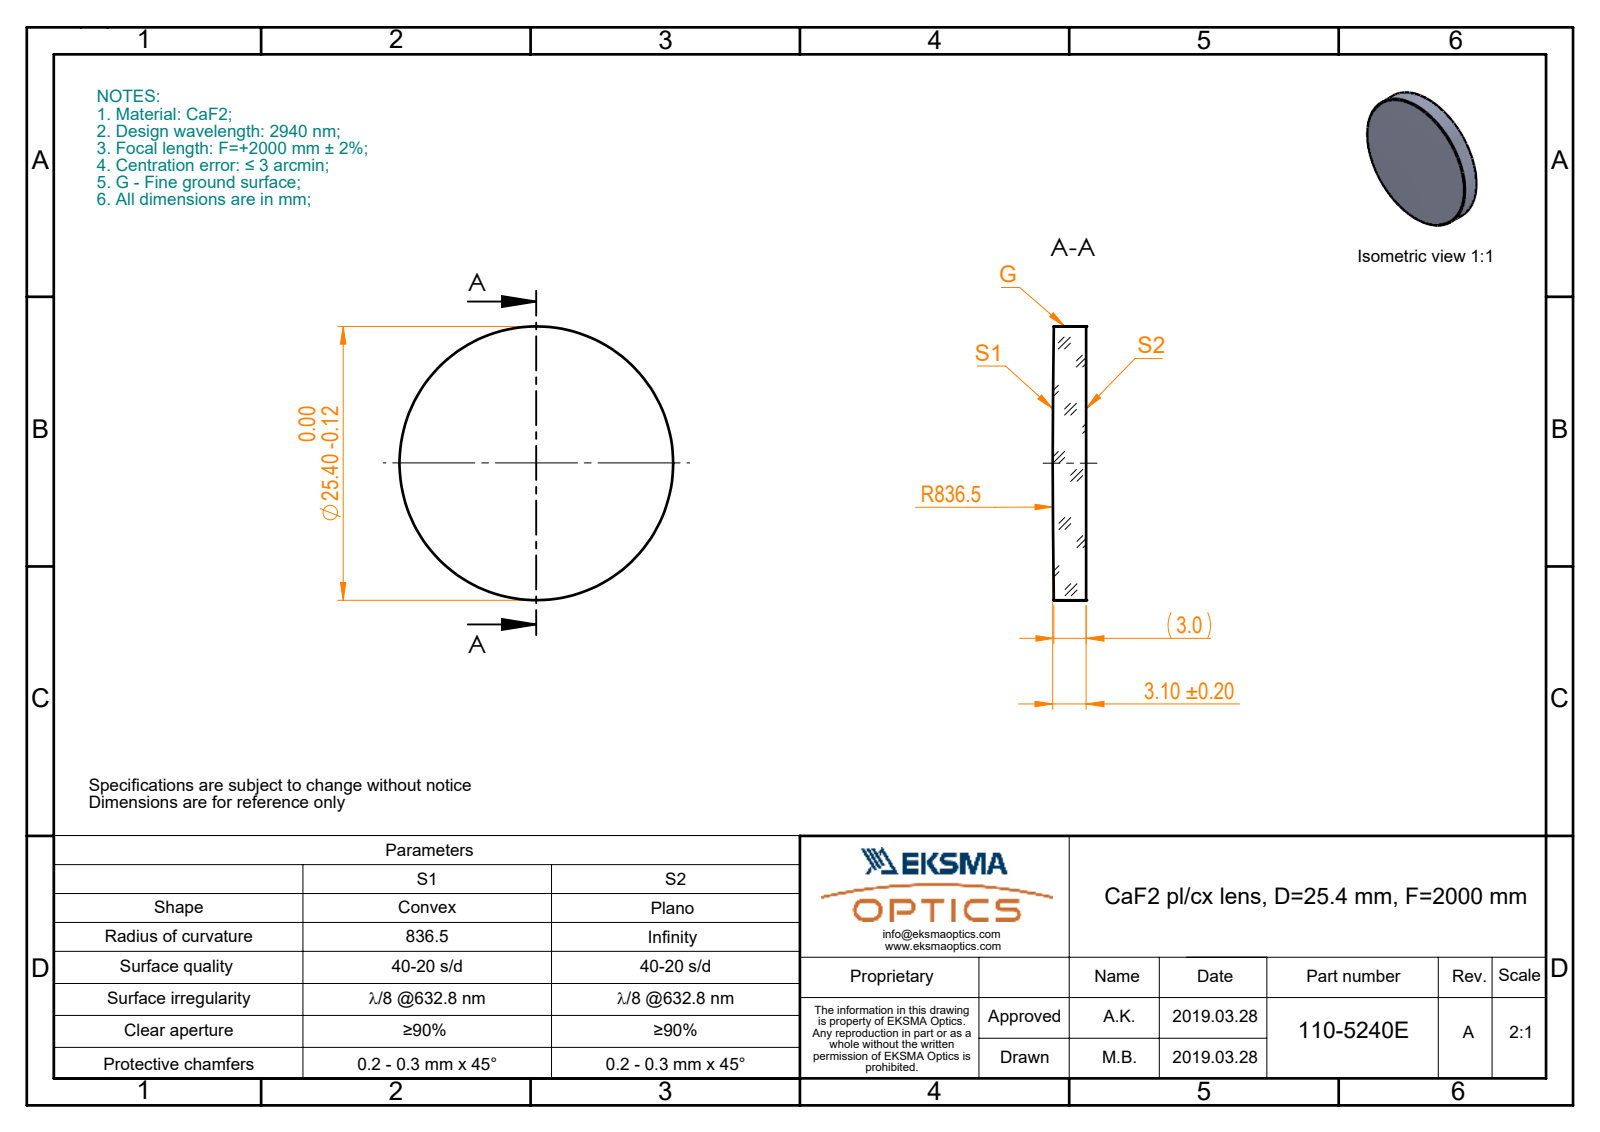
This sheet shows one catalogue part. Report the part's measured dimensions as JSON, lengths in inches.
{"part_name": "110-5240E CaF2 pl-cx 25.4 F2000", "step_written_by": "SolidWorks 2017 (CONFIG_CONTROL_DESIGN)", "units": "inches", "bodies": {"solids": 1, "faces": 5, "planar": 1, "cylindrical": 2, "other": 2}, "overall_size": [1, 1, 0.122], "volume_in3": 0.094, "surface_area_in2": 1.942, "round_bosses_or_shafts": [[1, 1]]}
